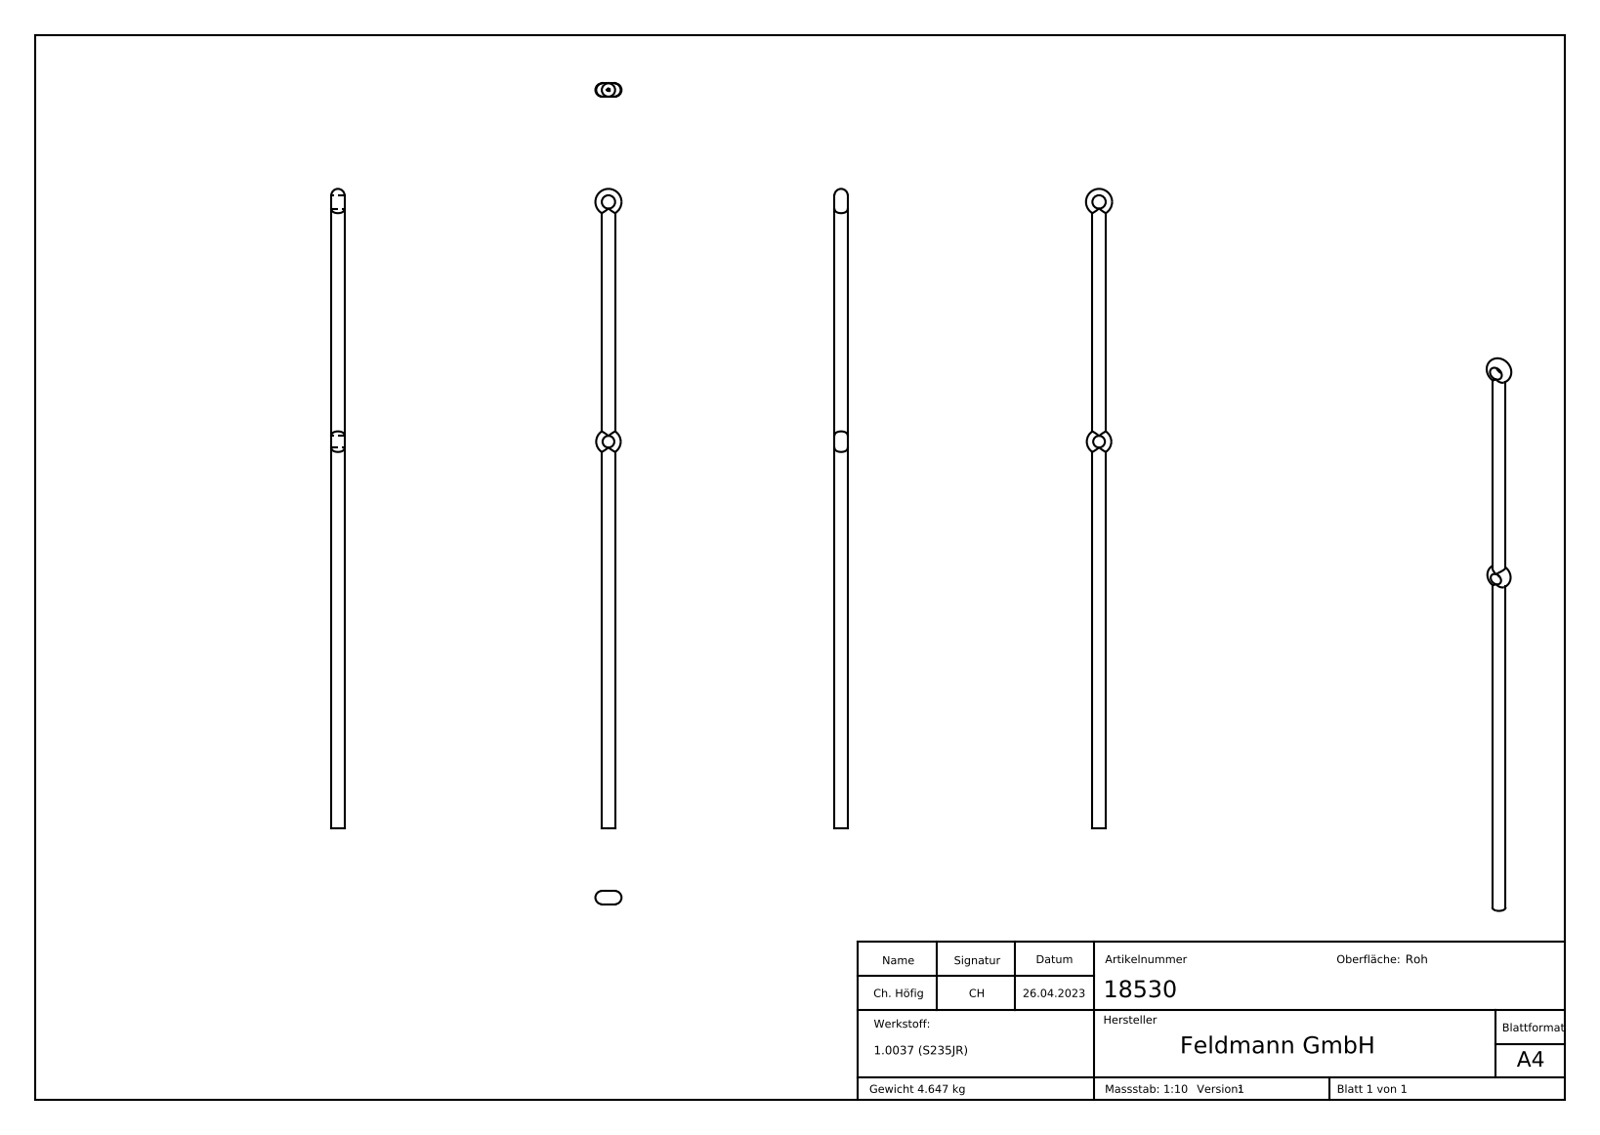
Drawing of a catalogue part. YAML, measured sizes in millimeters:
part_name: "18530"
step_written_by: "SolidWorks 2018 (CONFIG_CONTROL_DESIGN)"
units: millimeters
bodies: {solids: 1, faces: 192, planar: 89, cylindrical: 4, other: 99}
overall_size: [1200, 49, 25]
volume: 595850
surface_area: 99907
round_holes:
  - {diameter: 22, count: 1}
  - {diameter: 25, count: 1}
round_bosses_or_shafts:
  - {diameter: 25, count: 1}
face_to_face_distances: [0.5, 1.78, 1.21, 0.83, 1.32, 0.99, 0.67, 0.44, 2.45, 2.61]
hole_center_spacings: [450]
